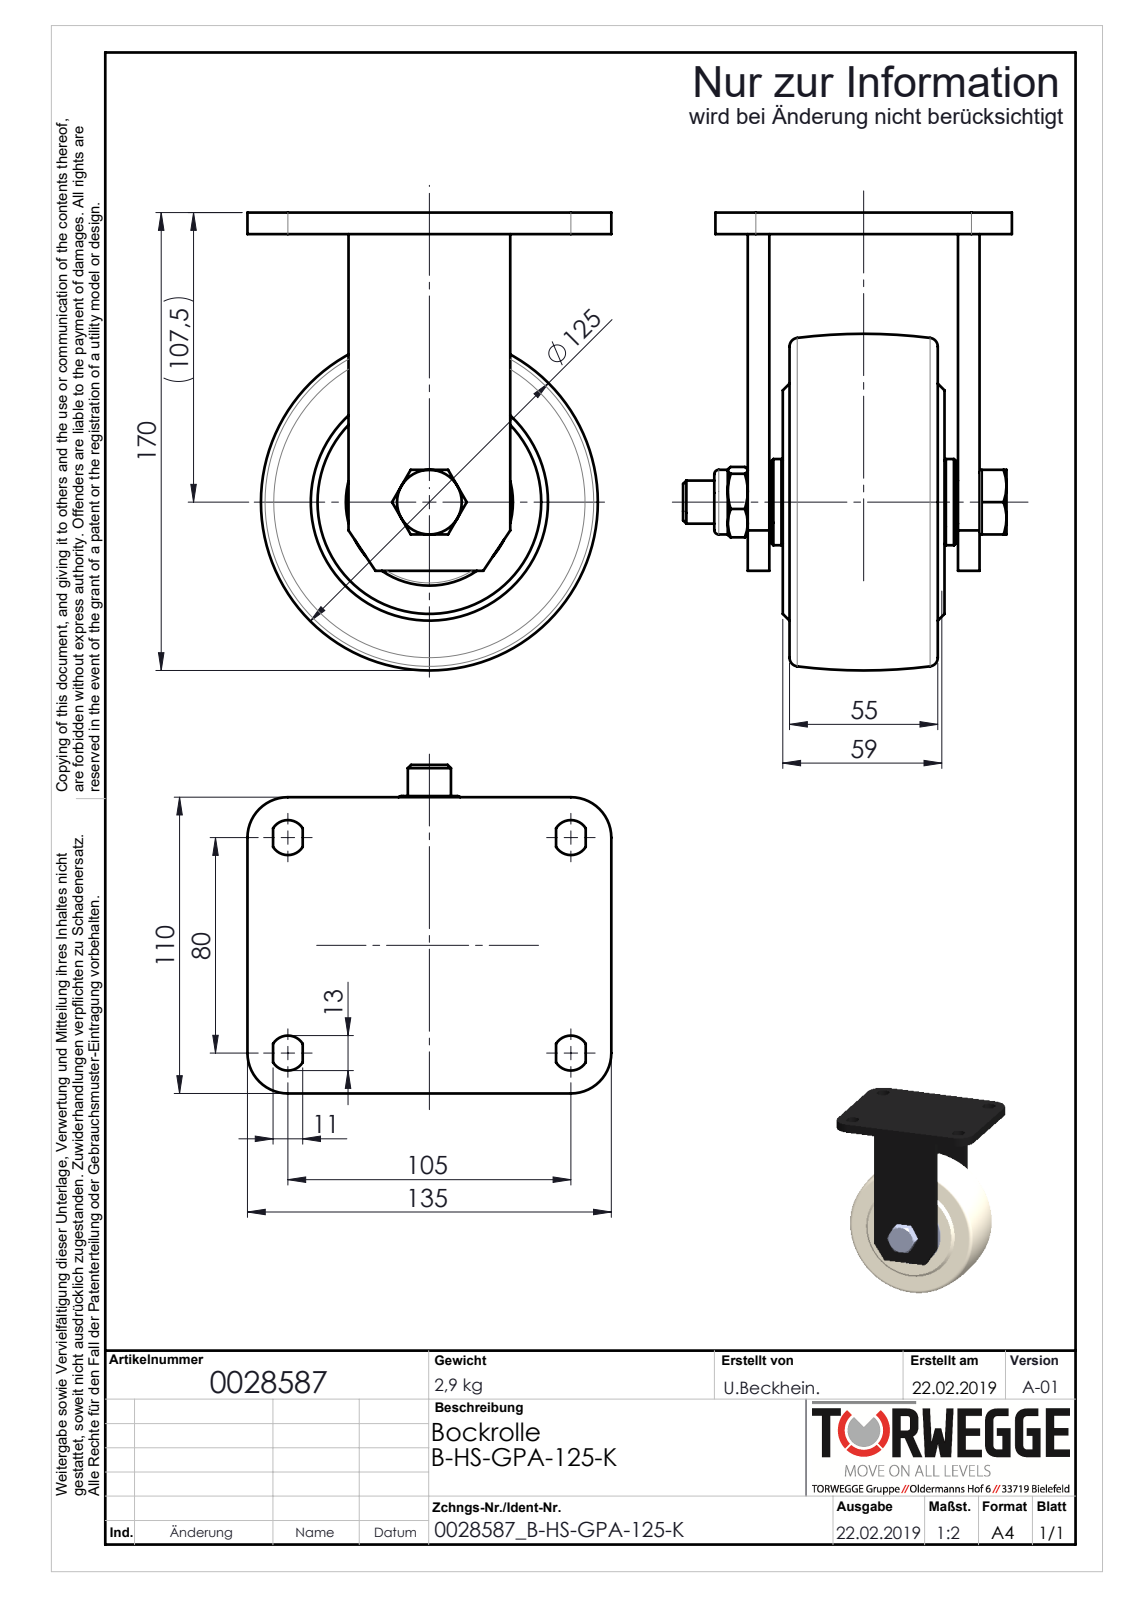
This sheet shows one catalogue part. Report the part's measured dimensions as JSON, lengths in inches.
{"part_name": "0028587_B-HS-GPA-125-K_(A-01)", "step_written_by": "SolidWorks 2018 (AUTOMOTIVE_DESIGN)", "units": "inches", "bodies": {"solids": 0, "faces": 199, "planar": 63, "cylindrical": 60, "other": 76}, "overall_size": [6.693, 5.315, 4.803], "round_holes": [[0.551, 1], [0.63, 1], [0.65, 1], [0.72, 1], [0.984, 1], [1.024, 1], [2.004, 1], [2.441, 1]], "round_bosses_or_shafts": [[1.421, 1], [1.26, 1], [0.945, 1]], "partial_cylinders_radius": [[0.256, 4], [0.591, 4]], "face_to_face_distances": [0.315, 3.071, 0.61, 2.776, 0.295, 2.461, 2.559, 0.512, 2.874, 0.197]}
